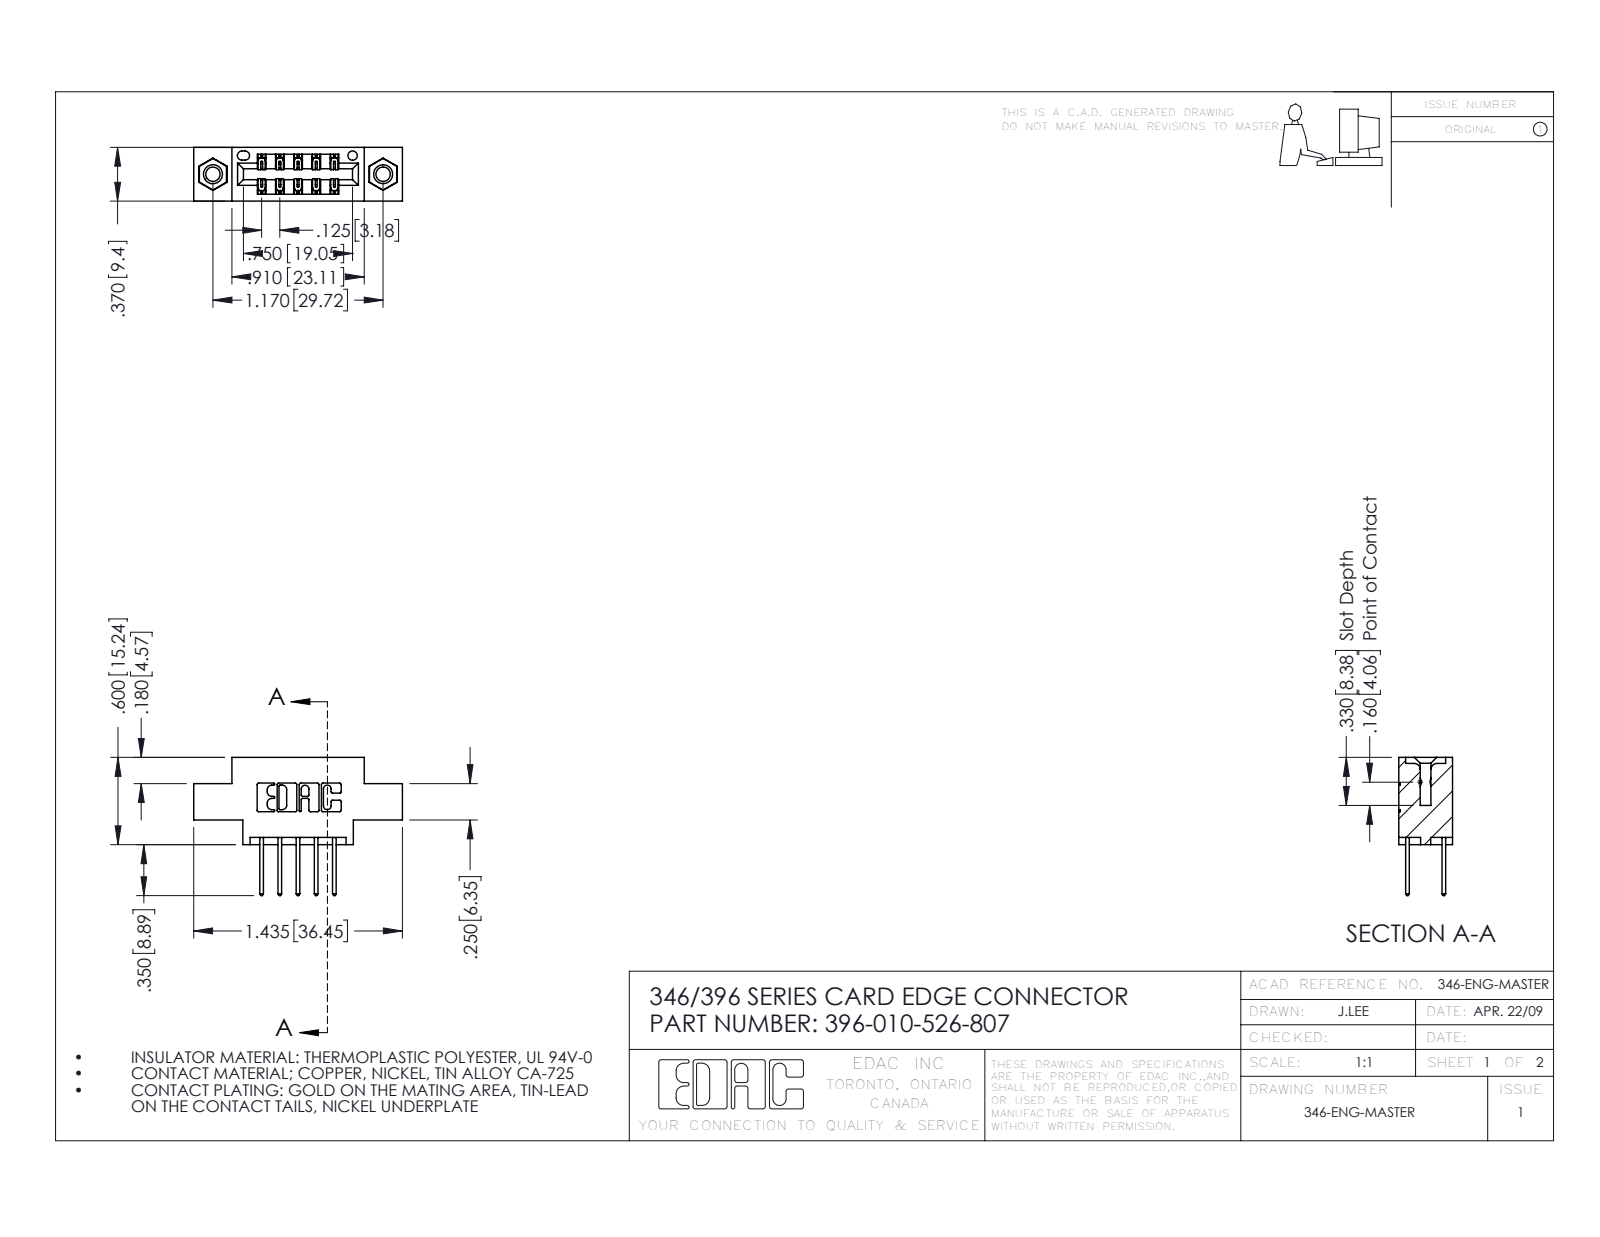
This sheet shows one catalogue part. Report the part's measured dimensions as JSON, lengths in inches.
{"part_name": "396-010-526-807; 345-292-001_345-293-126; 346 Part_0.170 Offset - 0.156 Dia-TI; 345-250-001_345-250-005-103", "step_written_by": "SolidWorks 2016 (CONFIG_CONTROL_DESIGN)", "units": "inches", "bodies": {"solids": 13, "faces": 706, "planar": 462, "cylindrical": 228, "other": 16}, "overall_size": [1.435, 0.95, 0.37], "volume_in3": 0.19, "surface_area_in2": 6.18, "round_holes": [[0.098, 2], [0.125, 2], [0.156, 2], [0.064, 1]], "round_bosses_or_shafts": [[0.155, 2]], "partial_cylinders_radius": [[0.01, 22], [0.006, 15], [0.01, 10], [0.007, 6], [0.031, 6], [0.026, 3], [0.014, 2], [0.022, 2]], "face_to_face_distances": [0.25, 0.37, 0.048, 0.322, 0.025, 0.072, 0.298, 0.222, 0.148, 0.275], "hole_center_spacings": [0.246, 0.969, 1.17]}
